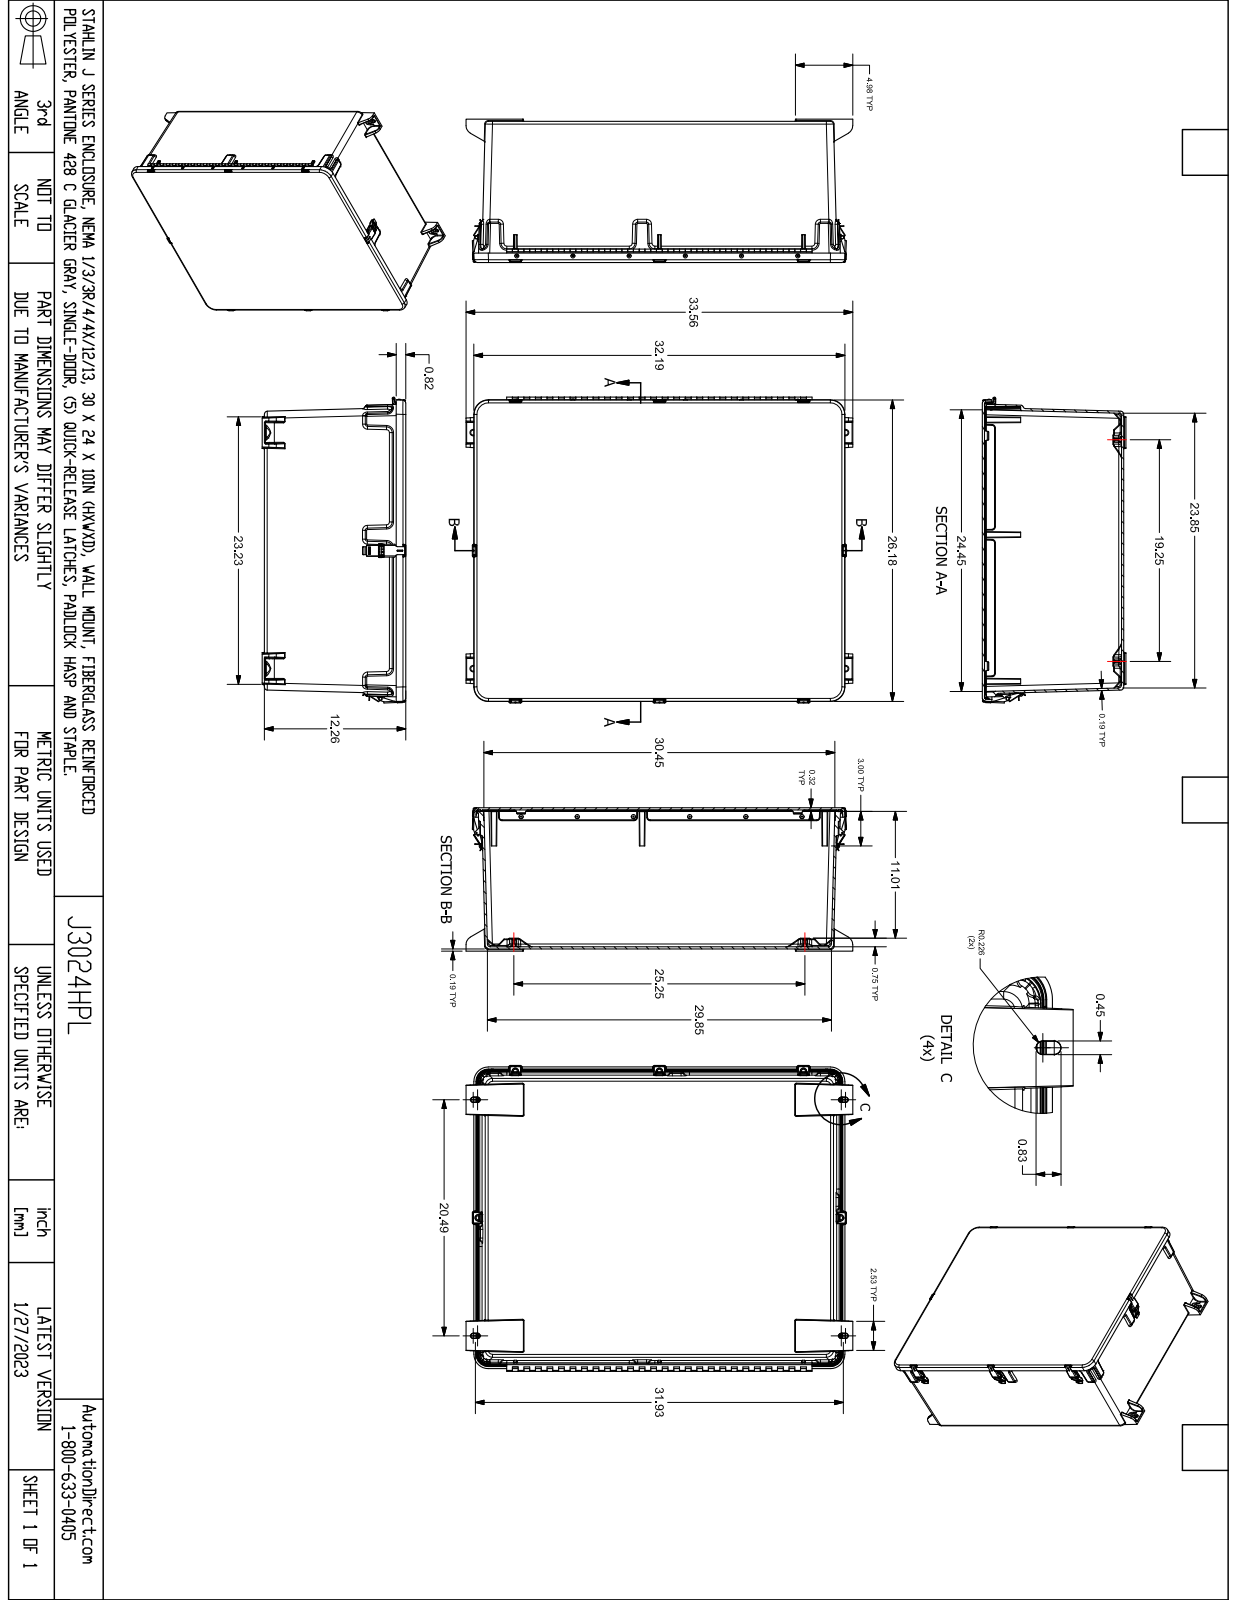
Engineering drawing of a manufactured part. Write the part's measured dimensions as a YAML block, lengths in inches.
part_name: "M3024HPL"
step_written_by: "SolidWorks 2018 (AUTOMOTIVE_DESIGN)"
units: inches
bodies: {solids: 42, faces: 3922, planar: 1158, cylindrical: 1428, other: 1336}
overall_size: [33.556, 26.559, 12.452]
volume: 611.4
surface_area: 6393
round_holes:
  - {diameter: 0.196, count: 12}
  - {diameter: 0.195, count: 10}
  - {diameter: 0.1, count: 6}
  - {diameter: 0.135, count: 6}
  - {diameter: 0.309, count: 4}
  - {diameter: 0.375, count: 3}
  - {diameter: 0.195, count: 2}
  - {diameter: 0.375, count: 2}
  - {diameter: 0.12, count: 1}
  - {diameter: 0.125, count: 1}
round_bosses_or_shafts:
  - {diameter: 0.357, count: 6}
  - {diameter: 0.187, count: 6}
  - {diameter: 0.5, count: 4}
  - {diameter: 0.375, count: 4}
  - {diameter: 0.3, count: 3}
  - {diameter: 0.185, count: 3}
  - {diameter: 0.185, count: 3}
  - {diameter: 0.135, count: 3}
partial_cylinders:
  - {radius: 0.05, count: 116}
  - {radius: 0.02, count: 106}
  - {radius: 0.063, count: 100}
  - {radius: 0.005, count: 84}
  - {radius: 0.125, count: 58}
  - {radius: 0.25, count: 58}
  - {radius: 0.062, count: 46}
  - {radius: 0.015, count: 40}
face_to_face_distances: [0.188, 12.076, 0.188, 12.264, 11.888, 0.294, 0.482, 0.439, 0.145, 0.043]
hole_center_spacings: [9.75, 4.875, 4.875, 14.625, 19.5, 0.429, 4.505, 10.127]
